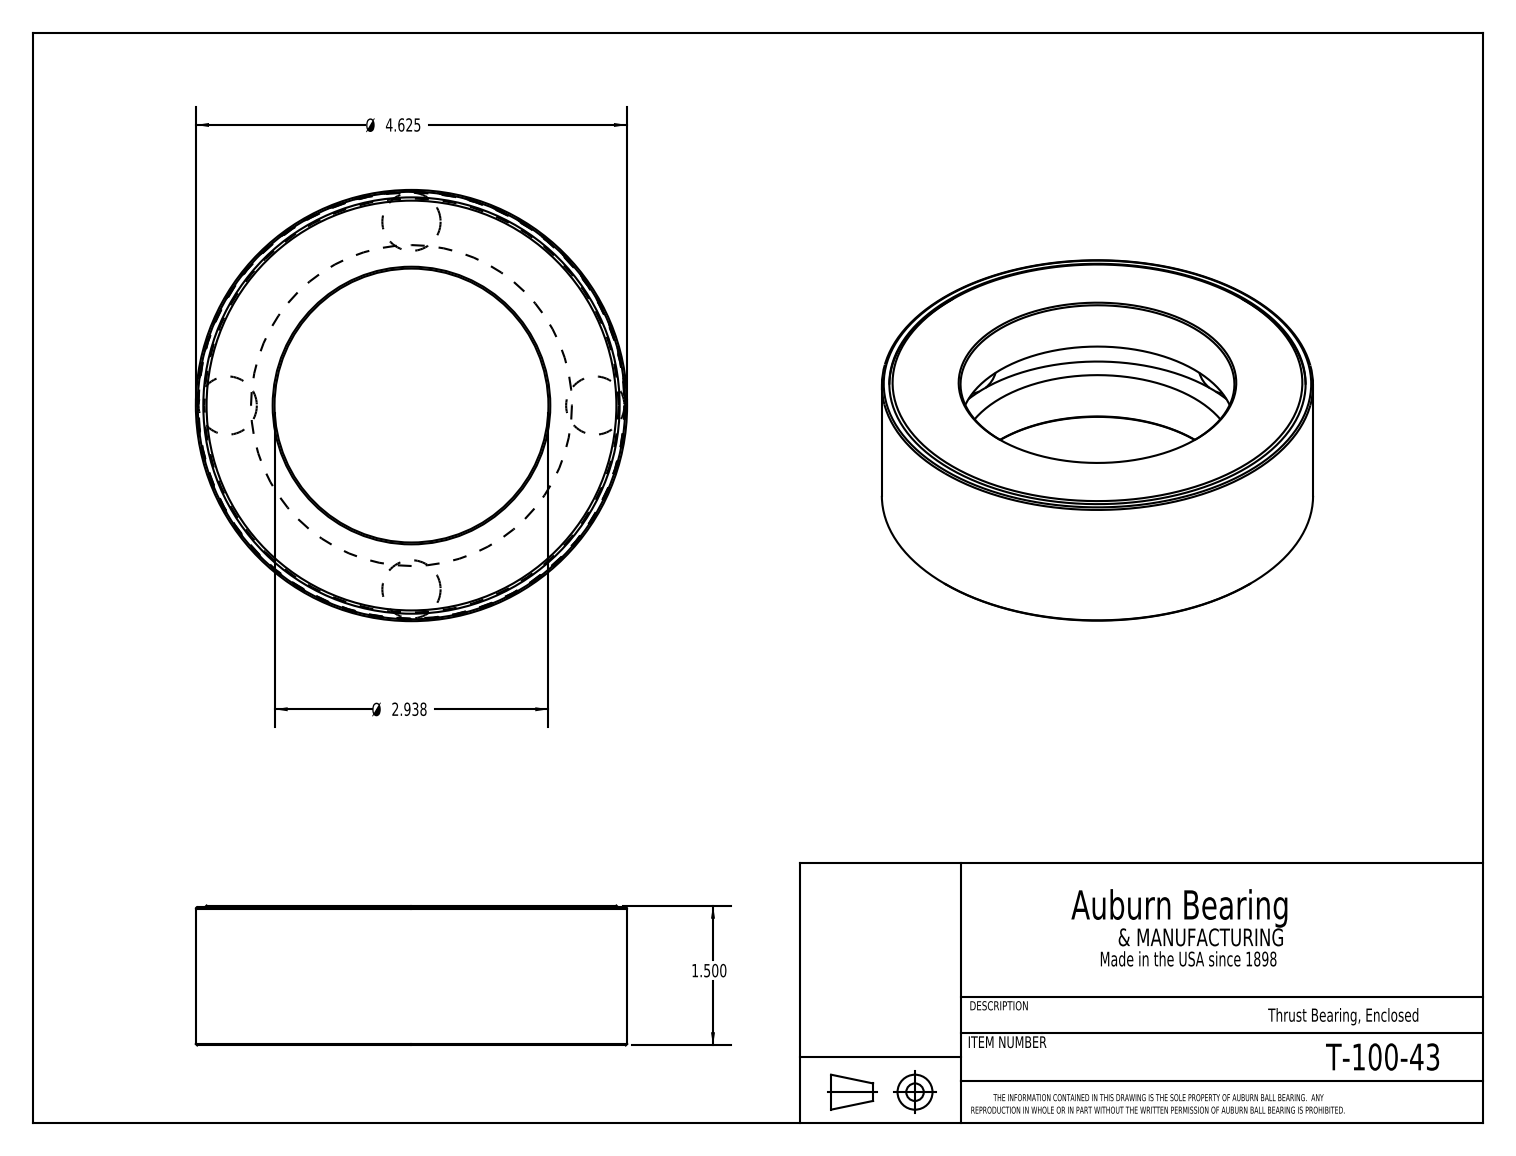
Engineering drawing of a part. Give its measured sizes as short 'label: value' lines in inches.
name: T-100-43
written by: SolidWorks 2016 (CONFIG_CONTROL_DESIGN)
unit: in
bodies: 6 solids, 28 faces (9 planar, 7 cylindrical, 12 other)
size: 4.625 × 4.625 × 1.5
volume: 10.71 in³; area: 100.1 in²
holes: 1× ⌀2.937, 1× ⌀4.465, 1× ⌀4.585
bosses: 1× ⌀4.625, 1× ⌀4.571
face distances: 1.5, 0.563, 0.937, 0.375, 1.485, 0.922, 0.548, 0.015, 1.465, 0.902
